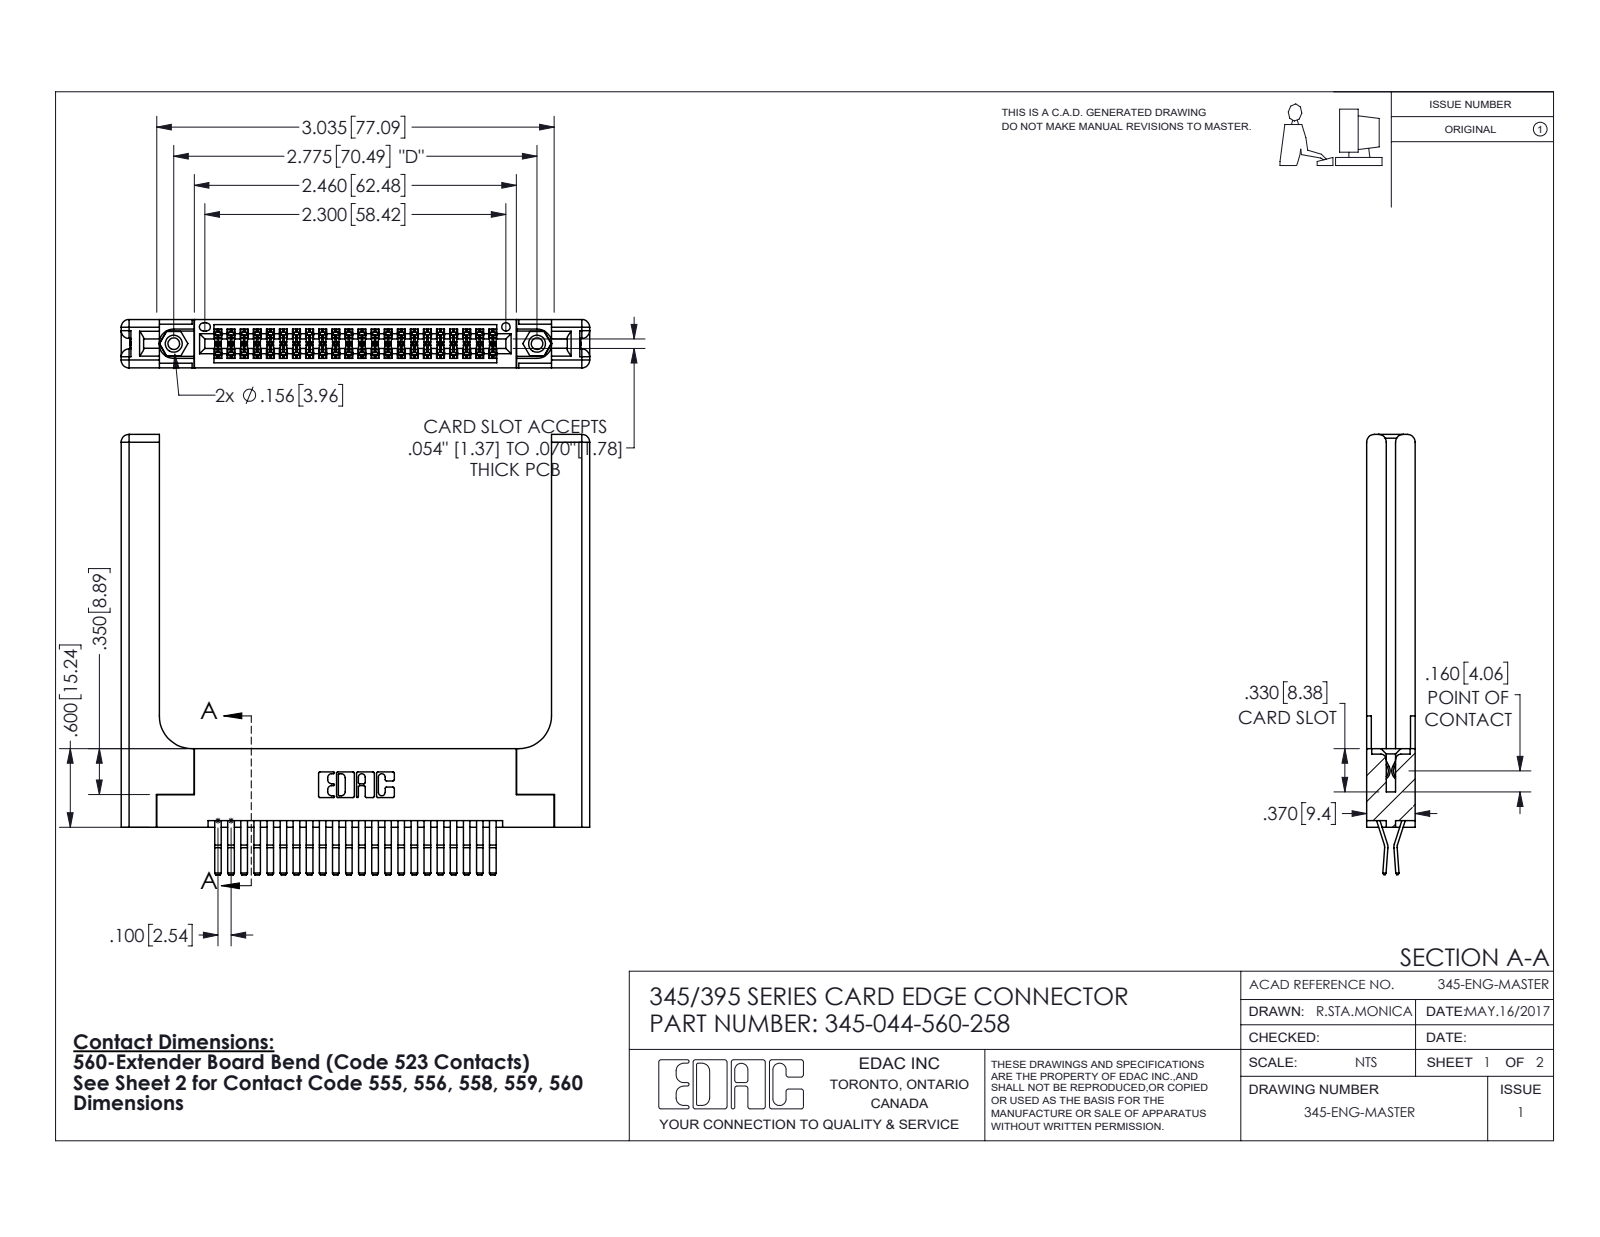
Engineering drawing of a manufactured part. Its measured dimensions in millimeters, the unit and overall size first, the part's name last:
Units: millimetres
Overall size (bounding box): 90.9 × 85.4 × 9.4
Round holes (diameter × count): ⌀2.3 ×2, ⌀3.2 ×2, ⌀4 ×2, ⌀1.6 ×1
Round bosses / shafts (diameter × count): ⌀3.9 ×2
Partial cylindrical surfaces — rounded edges, fillets, slot ends (radius × count): R0.2 ×66, R0.3 ×22, R1.5 ×16, R0.2 ×6, R0.8 ×6, R0.7 ×3, R0.3 ×2, R0.4 ×2
Main face-to-face distances: 9.4, 1.8, 7.6, 0.6, 5.1, 3.8, 3.8, 2, 5.7, 5.6
Hole centre spacings: 6.9, 64.5, 70.5
Volume: 17 400 mm³ · Surface area: 18 620 mm²
Bodies: 49 solids, 2670 faces (1680 planar, 930 cylindrical, 60 other)
Part name (STEP PRODUCT): 345-044-560-258; 345-292-001_560 Tail; 345-250-001_345-250-001-102; 345 Part_Flush Mounting Lugs - 0.156 Dia-TH (+1 more)
STEP written by: SolidWorks 2016 (CONFIG_CONTROL_DESIGN)
